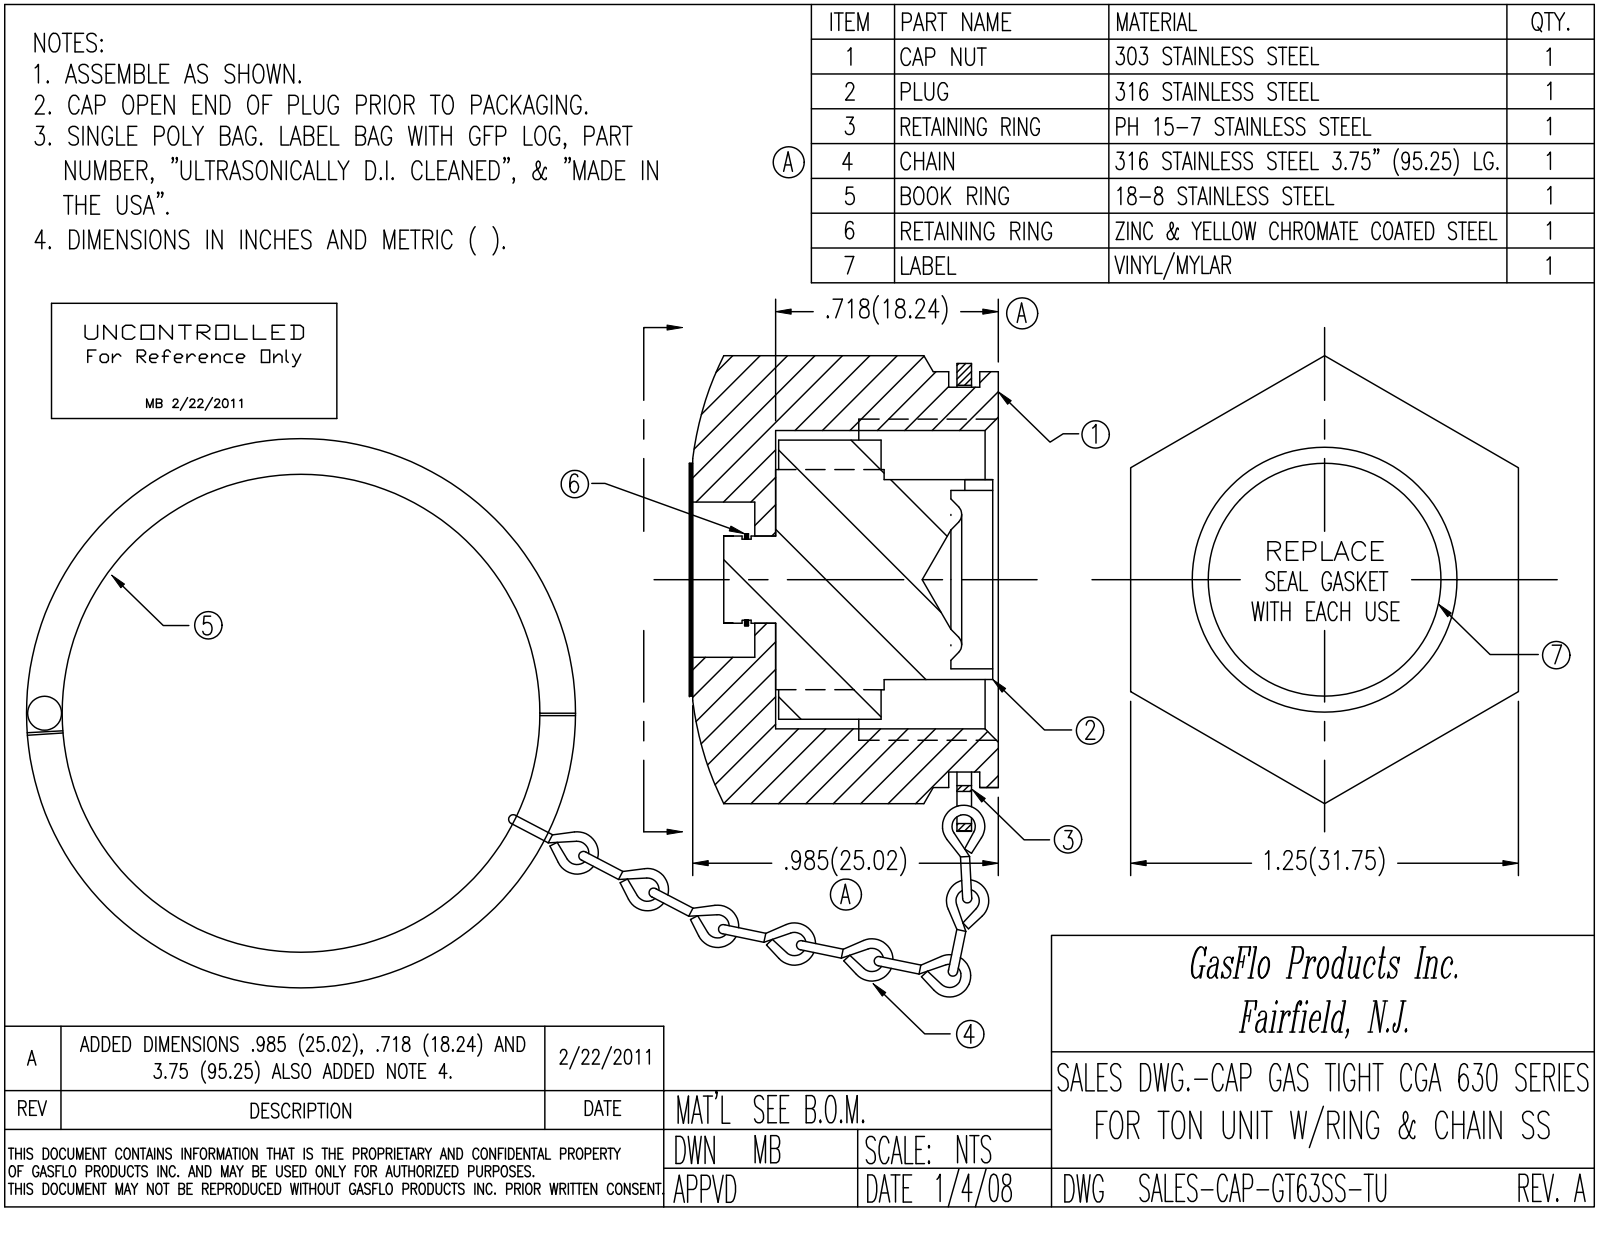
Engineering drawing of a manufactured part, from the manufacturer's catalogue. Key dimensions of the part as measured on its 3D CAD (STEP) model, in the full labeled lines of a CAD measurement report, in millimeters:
Part name (STEP PRODUCT): CAP-GT63SS-TU; PRT-002245_RING-1.540D-HALF; PRT-002255_SMALL PIN; ASY-000213_One Link Bent (+7 more)
STEP written by: SolidWorks 2018 (CONFIG_CONTROL_DESIGN)
Units: millimetres
Bodies: 16 solids, 912 faces (429 planar, 188 cylindrical, 295 other)
Overall size (bounding box): 134.7 × 65 × 38.2
Volume: 17 320 mm³ · Surface area: 13 020 mm²
Round holes (diameter × count): ⌀1 ×2, ⌀2 ×2, ⌀1.6 ×1, ⌀8 ×1, ⌀8.5 ×1, ⌀12.7 ×1, ⌀14.7 ×1, ⌀24.4 ×1, ⌀32.3 ×1
Round bosses / shafts (diameter × count): ⌀1.6 ×32, ⌀38.2 ×1, ⌀31.5 ×1, ⌀19.1 ×1, ⌀18 ×1, ⌀16.4 ×1, ⌀12.8 ×1, ⌀8.8 ×1
Partial cylindrical surfaces — rounded edges, fillets, slot ends (radius × count): R0.1 ×24, R0.7 ×4, R1.3 ×4, R6.4 ×4, R0.3 ×2, R1.9 ×1, R4.7 ×1, R17 ×1
Main face-to-face distances: 31.8, 6.8, 31.8, 21.6, 14.8, 22.9, 16.1, 1.3, 3.4, 25
Hole centre spacings: 18.6, 1.8, 4.2, 4.7, 4.7, 23.1, 23.2, 23.3
